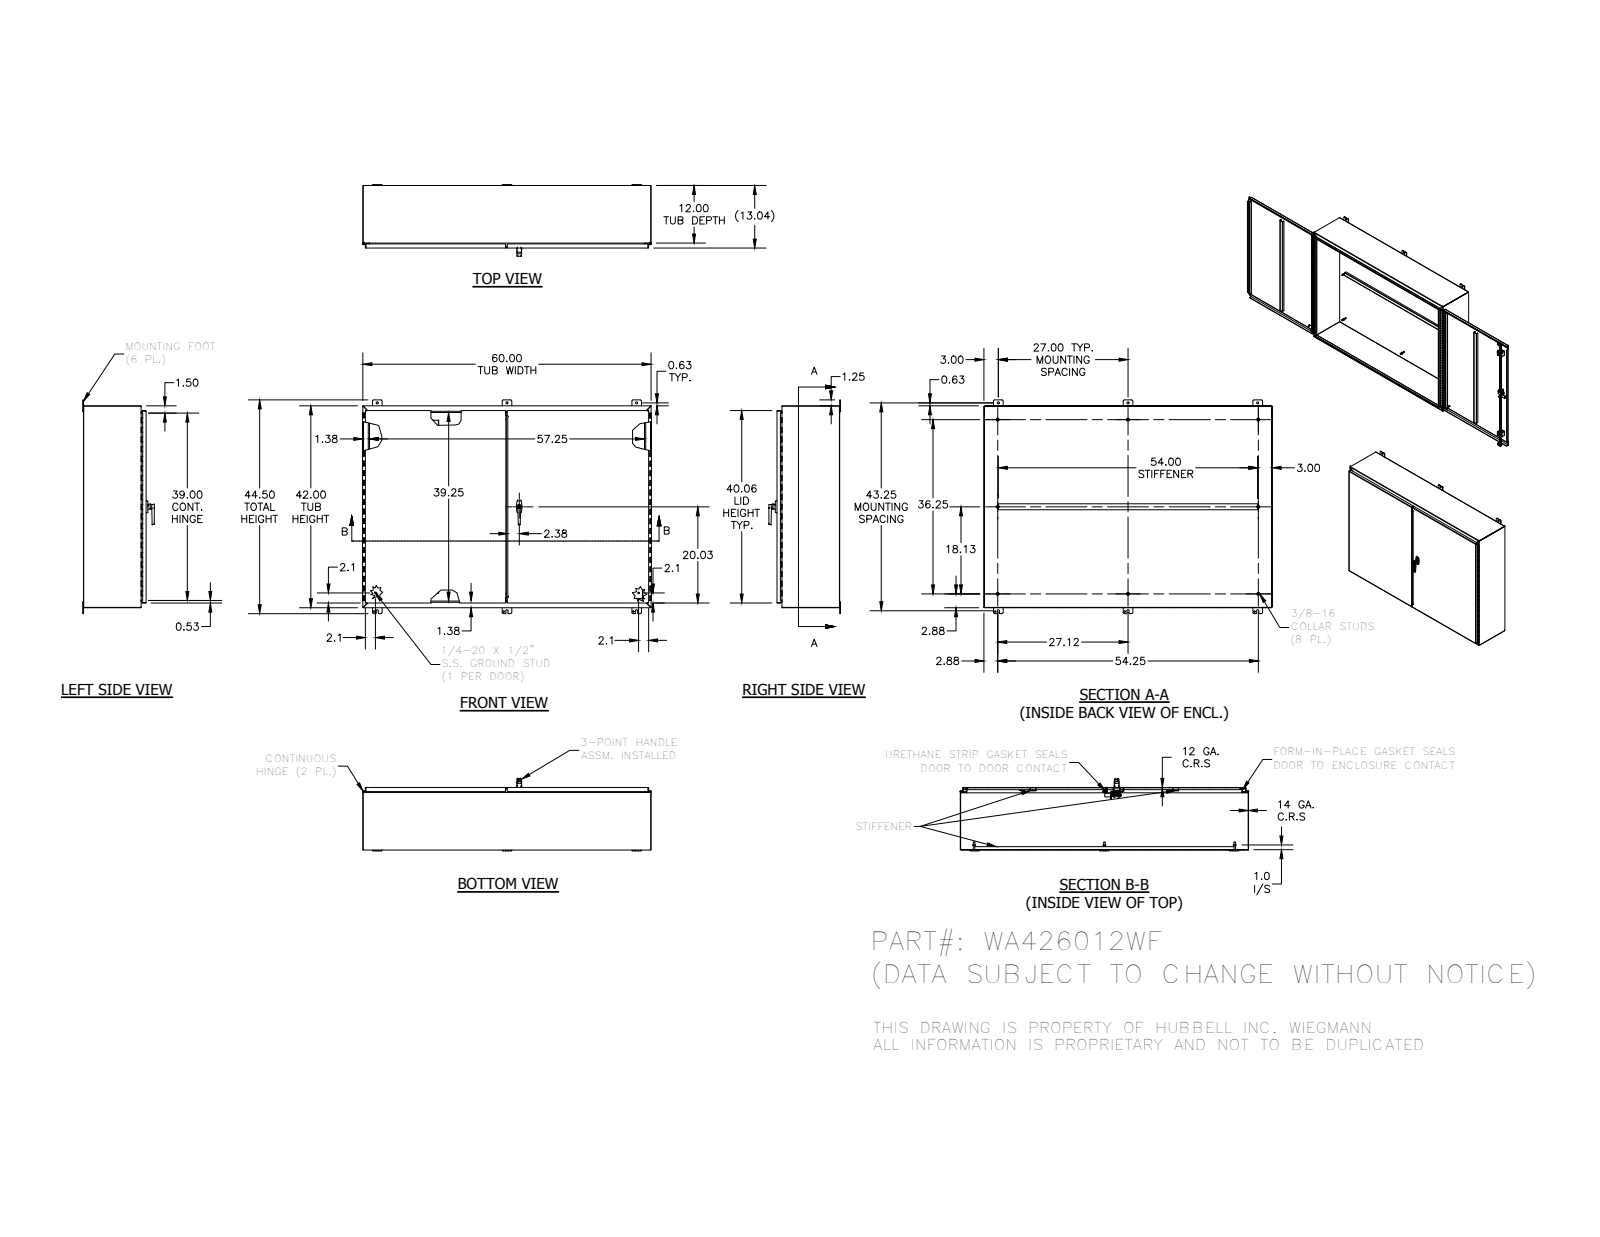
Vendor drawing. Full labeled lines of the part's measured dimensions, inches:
Part name (STEP PRODUCT): WA426012WFLRS; 34840; 38624; WA426012WFBTB (+8 more)
STEP written by: Autodesk Inventor 2014 (AUTOMOTIVE_DESIGN)
Units: inches
Bodies: 66 solids, 2782 faces (1594 planar, 696 cylindrical, 492 other)
Overall size (bounding box): 60.148 × 44.5 × 14.919
Volume: 751.2 in³ · Surface area: 17 900 in²
Round holes (diameter × count): ⌀0.276 ×8, ⌀0.083 ×6, ⌀0.313 ×6, ⌀0.438 ×6, ⌀0.2 ×4, ⌀0.125 ×2, ⌀0.159 ×2, ⌀0.241 ×2, ⌀0.25 ×2, ⌀0.252 ×2, ⌀0.4 ×2, ⌀0.407 ×2
Round bosses / shafts (diameter × count): ⌀0.625 ×8, ⌀0.33 ×8, ⌀0.157 ×7, ⌀0.25 ×4, ⌀0.115 ×4, ⌀1 ×2, ⌀0.563 ×2, ⌀0.526 ×2
Partial cylindrical surfaces — rounded edges, fillets, slot ends (radius × count): R0.031 ×34, R0.25 ×24, R0.105 ×23, R0.008 ×22, R0.016 ×22, R0.01 ×16, R0.05 ×14, R0.125 ×12
Main face-to-face distances: 0.074, 0.094, 12.942, 12.868, 13.035, 12.961, 41.926, 59.926, 41.852, 42
Hole centre spacings: 27, 49.93, 0.293, 0.201, 1.593, 26.352, 27.724, 42
